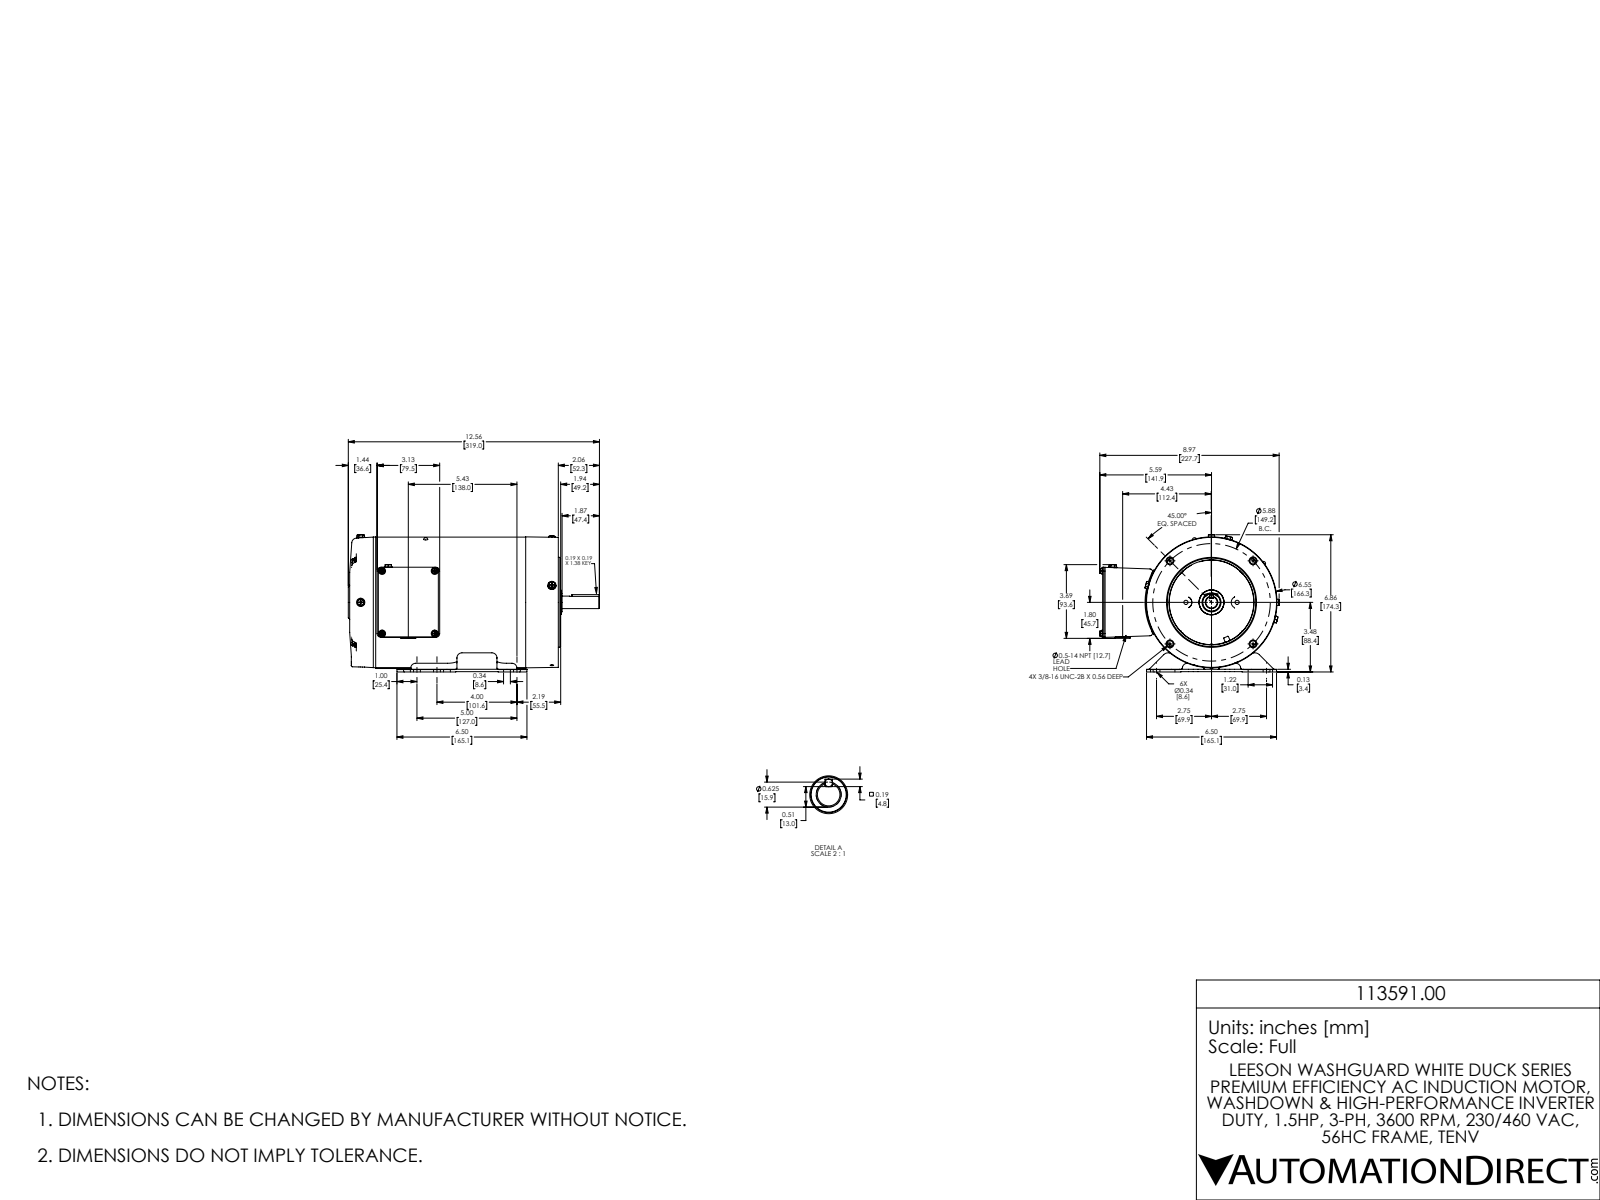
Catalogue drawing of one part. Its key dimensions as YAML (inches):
part_name: "034918-750_Rev04_56HC_1P5HP wo Front Bell COMPLETE A Coord"
step_written_by: "SolidWorks 2017 (AUTOMOTIVE_DESIGN)"
units: inches
bodies: {solids: 35, faces: 3730, planar: 907, cylindrical: 602, other: 2221}
overall_size: [12.557, 8.966, 6.861]
volume: 79.14
surface_area: 886.4
round_holes:
  - {diameter: 0.177, count: 7}
  - {diameter: 0.19, count: 7}
  - {diameter: 0.147, count: 6}
  - {diameter: 0.34, count: 6}
  - {diameter: 0.159, count: 4}
  - {diameter: 0.25, count: 4}
  - {diameter: 0.26, count: 4}
  - {diameter: 0.272, count: 4}
  - {diameter: 0.313, count: 4}
  - {diameter: 0.173, count: 3}
  - {diameter: 0.103, count: 2}
  - {diameter: 0.128, count: 2}
round_bosses_or_shafts:
  - {diameter: 0.19, count: 10}
  - {diameter: 0.414, count: 6}
  - {diameter: 0.5, count: 4}
  - {diameter: 0.399, count: 4}
  - {diameter: 0.348, count: 4}
  - {diameter: 0.166, count: 4}
  - {diameter: 0.164, count: 4}
  - {diameter: 0.112, count: 2}
partial_cylinders:
  - {radius: 0.06, count: 103}
  - {radius: 0.03, count: 61}
  - {radius: 0.17, count: 16}
  - {radius: 0.25, count: 10}
  - {radius: 0.01, count: 8}
  - {radius: 0.19, count: 8}
  - {radius: 0.5, count: 8}
  - {radius: 0.38, count: 4}
face_to_face_distances: [0.015, 0.119, 1.05, 0.063, 0.104, 0.059, 0.122, 0.19, 0.12, 0.134]
hole_center_spacings: [4.078, 0.11, 1.878, 2.095, 2.125, 2.193, 2.225, 2.63]
